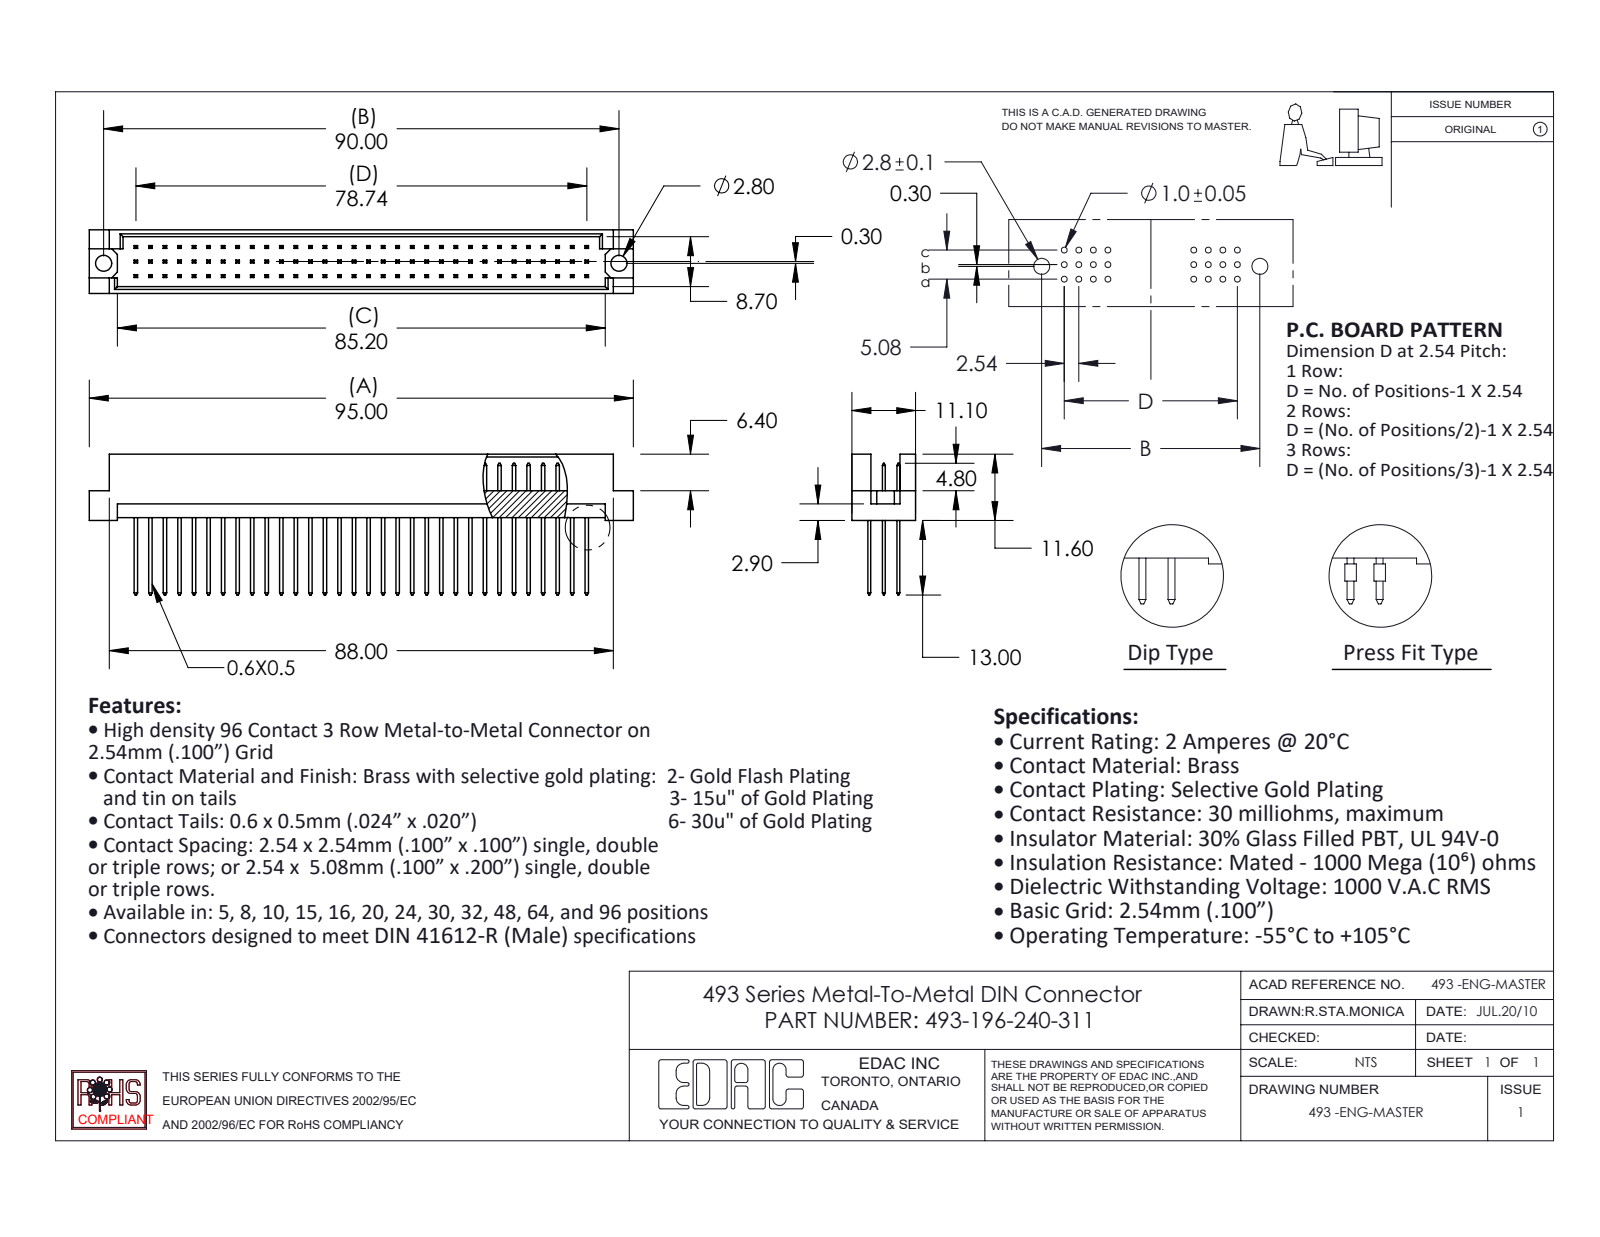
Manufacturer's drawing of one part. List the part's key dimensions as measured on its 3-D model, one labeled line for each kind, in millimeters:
Part name (STEP PRODUCT): 493-196-240-311; 493 Part_96; 493-290_40
STEP written by: SolidWorks 2020 (CONFIG_CONTROL_DESIGN)
Units: millimetres
Bodies: 97 solids, 1780 faces (1776 planar, 4 cylindrical, 0 other)
Overall size (bounding box): 95 × 24.6 × 11.1
Volume: 6 310 mm³ · Surface area: 11 295 mm²
Round holes (diameter × count): ⌀2.8 ×2
Main face-to-face distances: 2.54, 5.08, 0.5, 1.2, 9.9, 2.76, 3.26, 5.3, 5.8, 7.84
Hole centre spacings: 90
